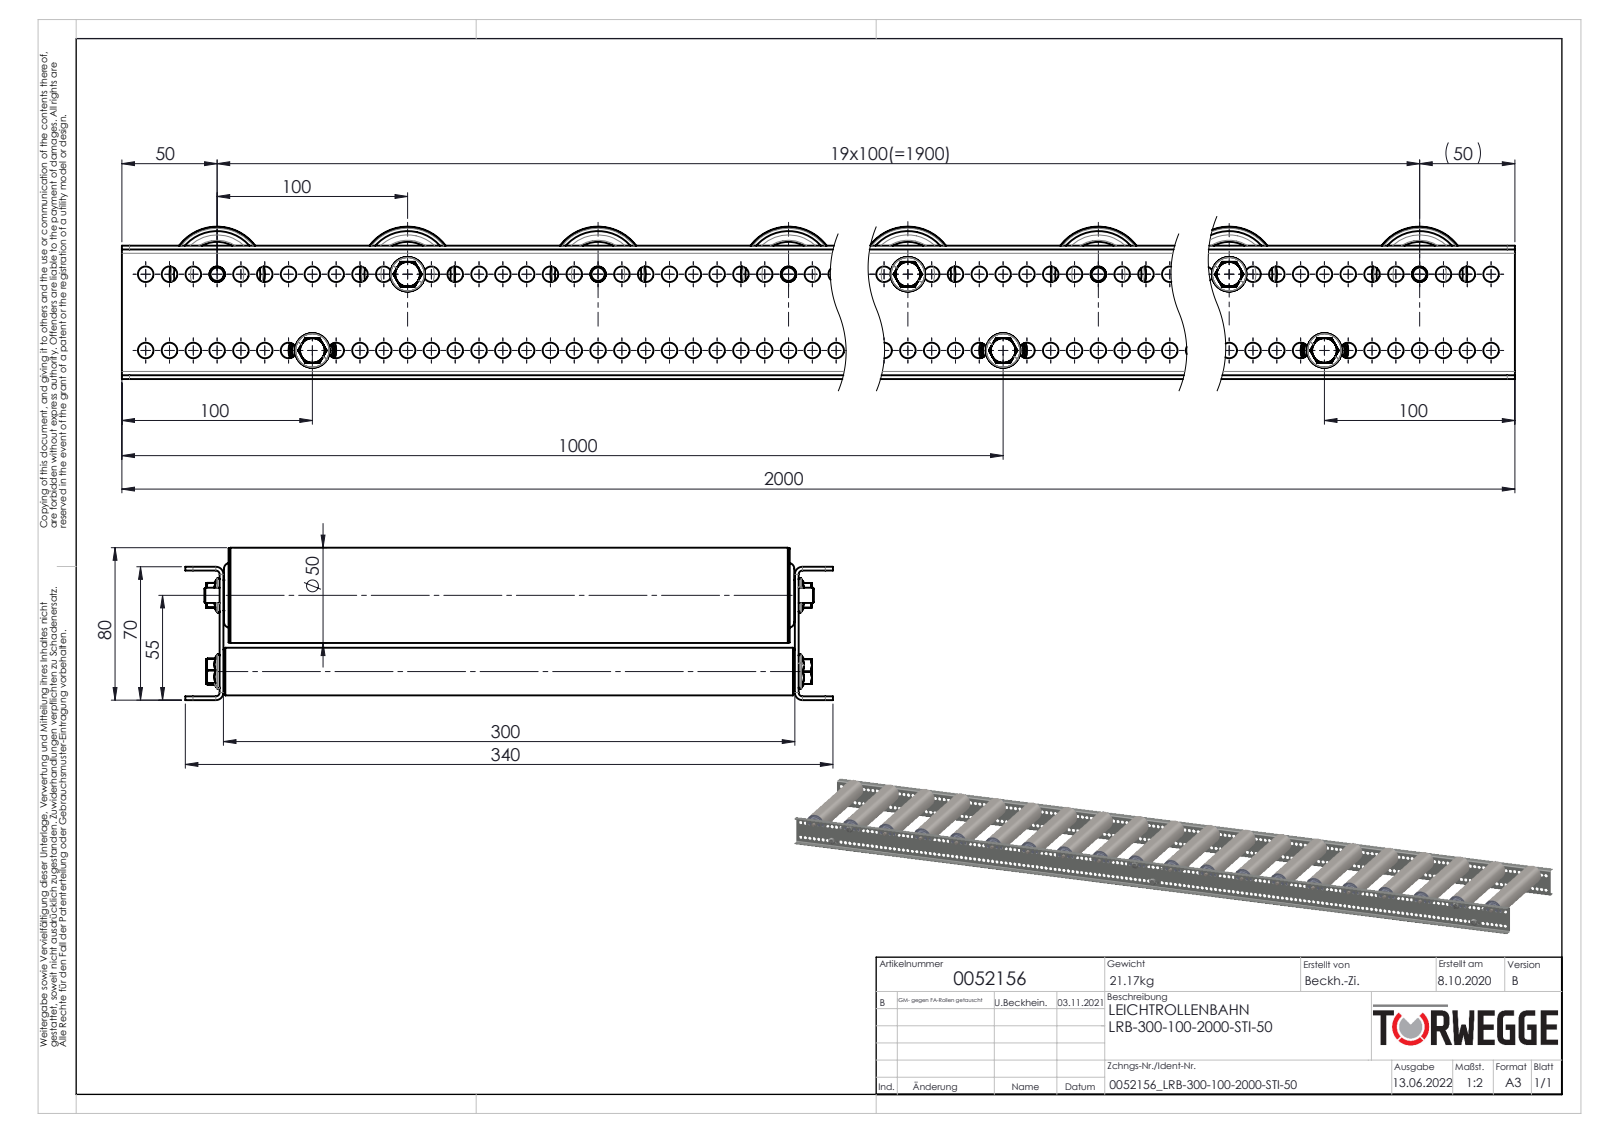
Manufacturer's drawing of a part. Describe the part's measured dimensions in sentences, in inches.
The part is named "Sicherungsring_DIN471_8x0.8_Circlip DIN 471 - 8 x 0.8; TRG-50x1,5-STI-A12-IGM8-EL=KFG_0022777TWG_TRG-50x1,5-STI-A12-IGM8-EL=300; 0026293_Typ-TRG-50x1,5-12; 0052156 (+8 more)". Its 3-D file was written by "SolidWorks 2020 (AUTOMOTIVE_DESIGN)". It is 476 solids with 8806 faces: 1716 planar, 3328 cylindrical and 3762 other. Overall it measures 78.74 by 13.386 by 3.15 inches. Its volume is 183.2 cubic inches and its surface area 5 427 square inches. Round holes: 318 of diameter 0.323, 20 of diameter 0.673, 20 of diameter 0.728, 20 of diameter 1.091, 20 of diameter 1.783, 20 of diameter 1.85, 17 of diameter 0.299, 6 of diameter 0.268, 3 of diameter 0.472, 3 of diameter 0.48, 3 of diameter 0.756, 3 of diameter 0.827. Round bosses or shafts: 23 of diameter 0.315, 20 of diameter 1.969, 20 of diameter 1.949, 20 of diameter 1.862, 20 of diameter 1.169, 20 of diameter 1.079, 20 of diameter 1.075, 20 of diameter 0.63. Partial cylindrical surfaces (rounded edges, fillets, slot ends): 34 of radius 0.024, 34 of radius 0.03, 34 of radius 0.096, 17 of radius 0.192, 17 of radius 0.276, 12 of radius 0.098, 8 of radius 0.157, 4 of radius 0.079. The main face-to-face distances are 0.079, 11.89, 2.677, 11.811, 11.969, 2.756, 2.598, 0.039, 0.091, 11.878. The hole center spacings are 0.492, 0.984, 1.476, 1.969, 2.461, 2.953, 3.445, 3.937.
